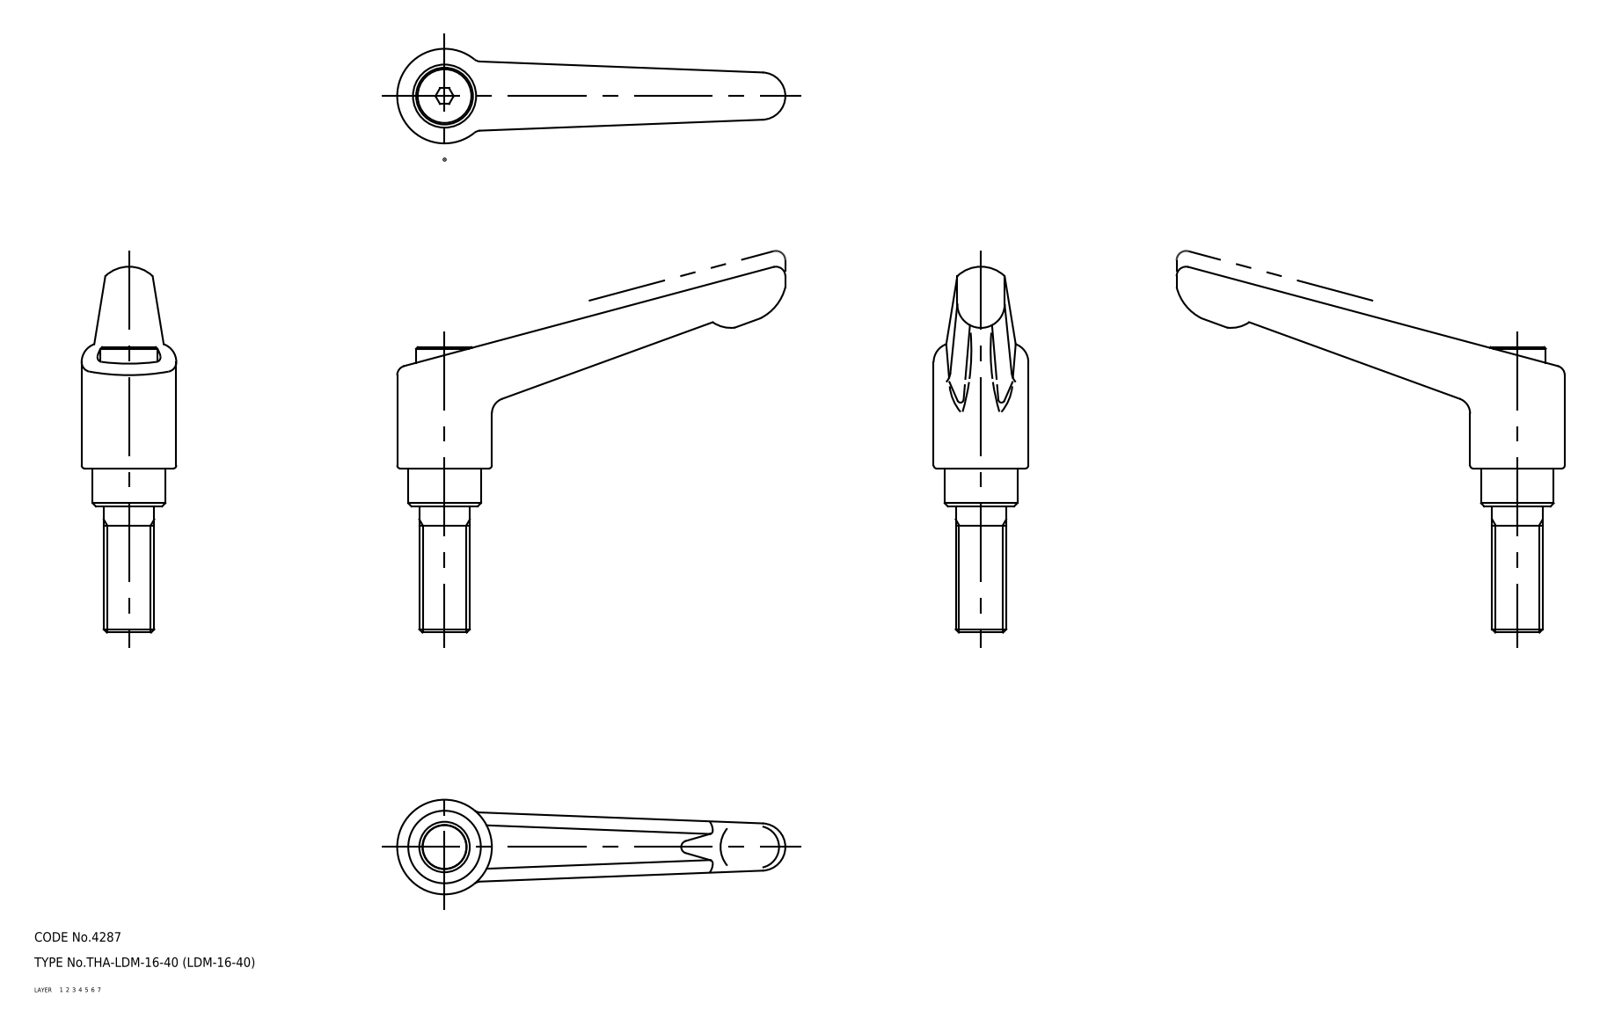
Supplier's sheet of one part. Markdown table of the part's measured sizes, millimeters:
| quantity | value |
| --- | --- |
| part name | sleeve; screw; handle; LDM_16_40_12330_36 |
| STEP written by | CADfix (AUTOMOTIVE_DESIGN) |
| units | millimeters |
| bodies | 3 solids, 92 faces (0 planar, 0 cylindrical, 92 other) |
| overall size | 123 × 116 × 30 |
| volume | 53 534 mm³ |
| surface area | 19 392 mm² |
